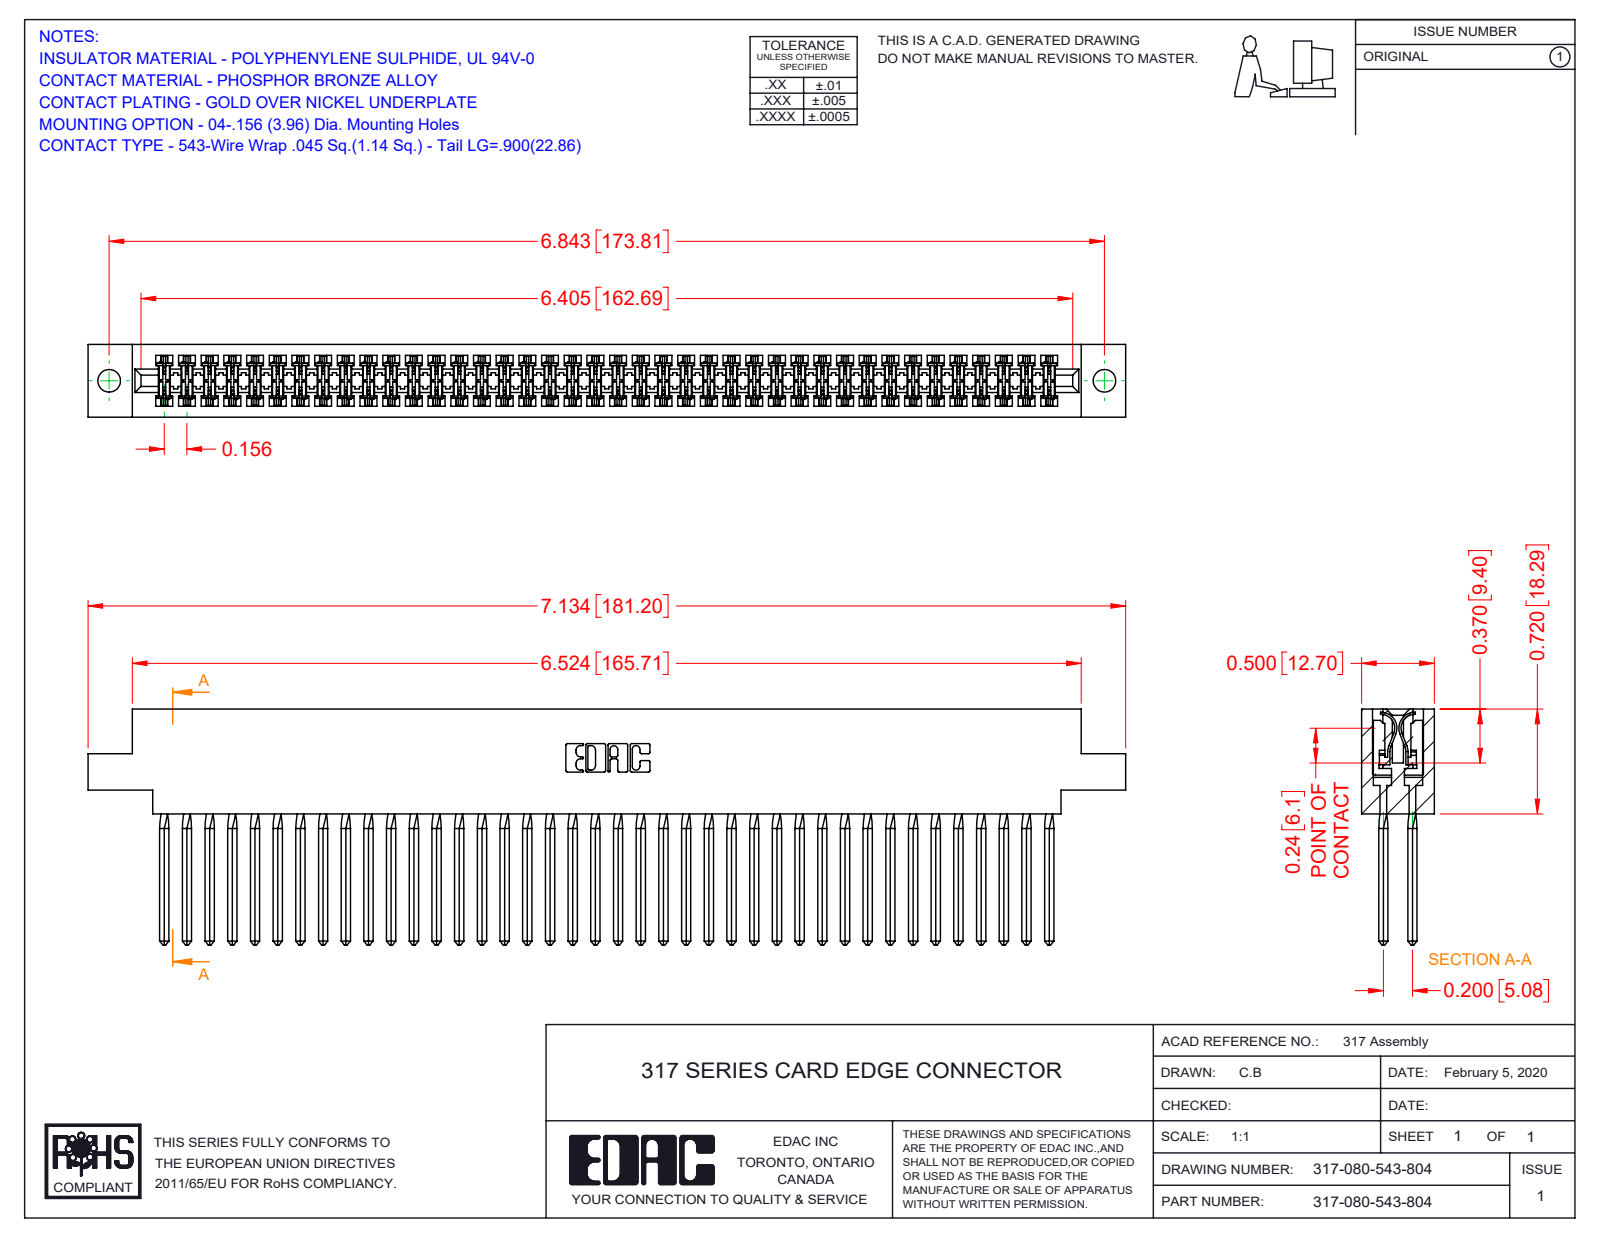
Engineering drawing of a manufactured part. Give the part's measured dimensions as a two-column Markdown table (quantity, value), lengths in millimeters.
| quantity | value |
| --- | --- |
| part name | 317-080-543-804; 317-290-001_543; 317 Part_.156 Dia - TH |
| STEP written by | SolidWorks 2016 (CONFIG_CONTROL_DESIGN) |
| units | millimeters |
| bodies | 81 solids, 7222 faces (5898 planar, 1004 cylindrical, 320 other) |
| overall size | 181.2 × 41.1 × 12.7 |
| volume | 30 660 mm³ |
| surface area | 46 250 mm² |
| round holes (diameter × count) | 4 × 2 |
| partial cylindrical surfaces (radius × count) | 0.4 × 160, 0.3 × 22, 0.2 × 6, 0.8 × 6, 0.7 × 3, 2.4 × 2, 2.5 × 2, 2.8 × 2 |
| main face-to-face distances | 12.7, 1.9, 10.8, 8.9, 2.8, 5, 2.4, 5.1, 2.9, 3.3 |
| hole center spacings | 173.8 |
